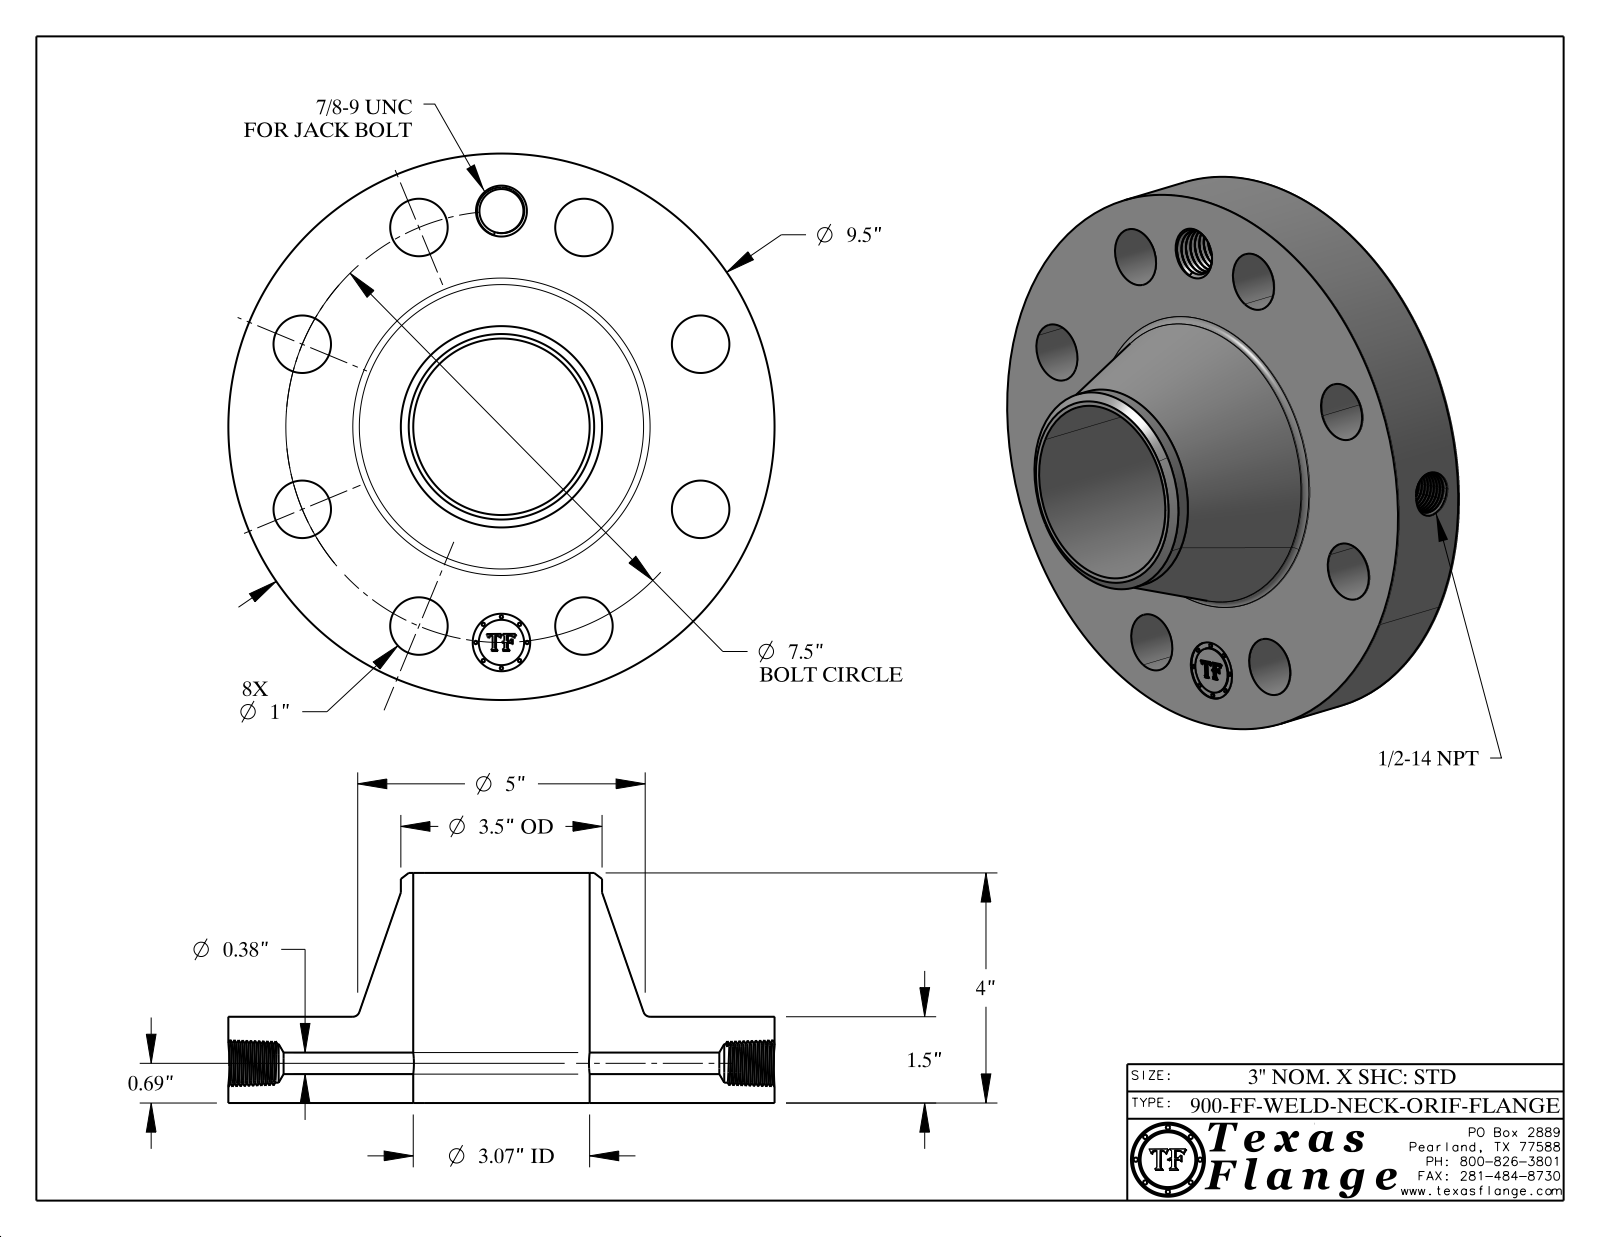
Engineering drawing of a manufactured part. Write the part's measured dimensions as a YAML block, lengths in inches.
part_name: "900-FF-WELD-NECK"
step_written_by: "CATIA V5 STEP AP214 (AUTOMOTIVE_DESIGN)"
units: inches
bodies: {solids: 1, faces: 756, planar: 368, cylindrical: 88, other: 300}
overall_size: [9.5, 9.5, 4]
volume: 99.42
surface_area: 274.9
round_holes:
  - {diameter: 1, count: 9}
  - {diameter: 0.375, count: 1}
  - {diameter: 0.672, count: 1}
  - {diameter: 0.766, count: 1}
  - {diameter: 3.068, count: 1}
round_bosses_or_shafts:
  - {diameter: 0.061, count: 8}
  - {diameter: 9.5, count: 1}
  - {diameter: 3.5, count: 1}
  - {diameter: 0.788, count: 1}
face_to_face_distances: [1.5, 4, 2.5, 1.485, 0.015, 2.515, 0.298, 0.293, 0.054, 0.248]
hole_center_spacings: [3.75, 2.87, 5.303, 6.929, 7.5, 1.463, 4.167, 6.236]
